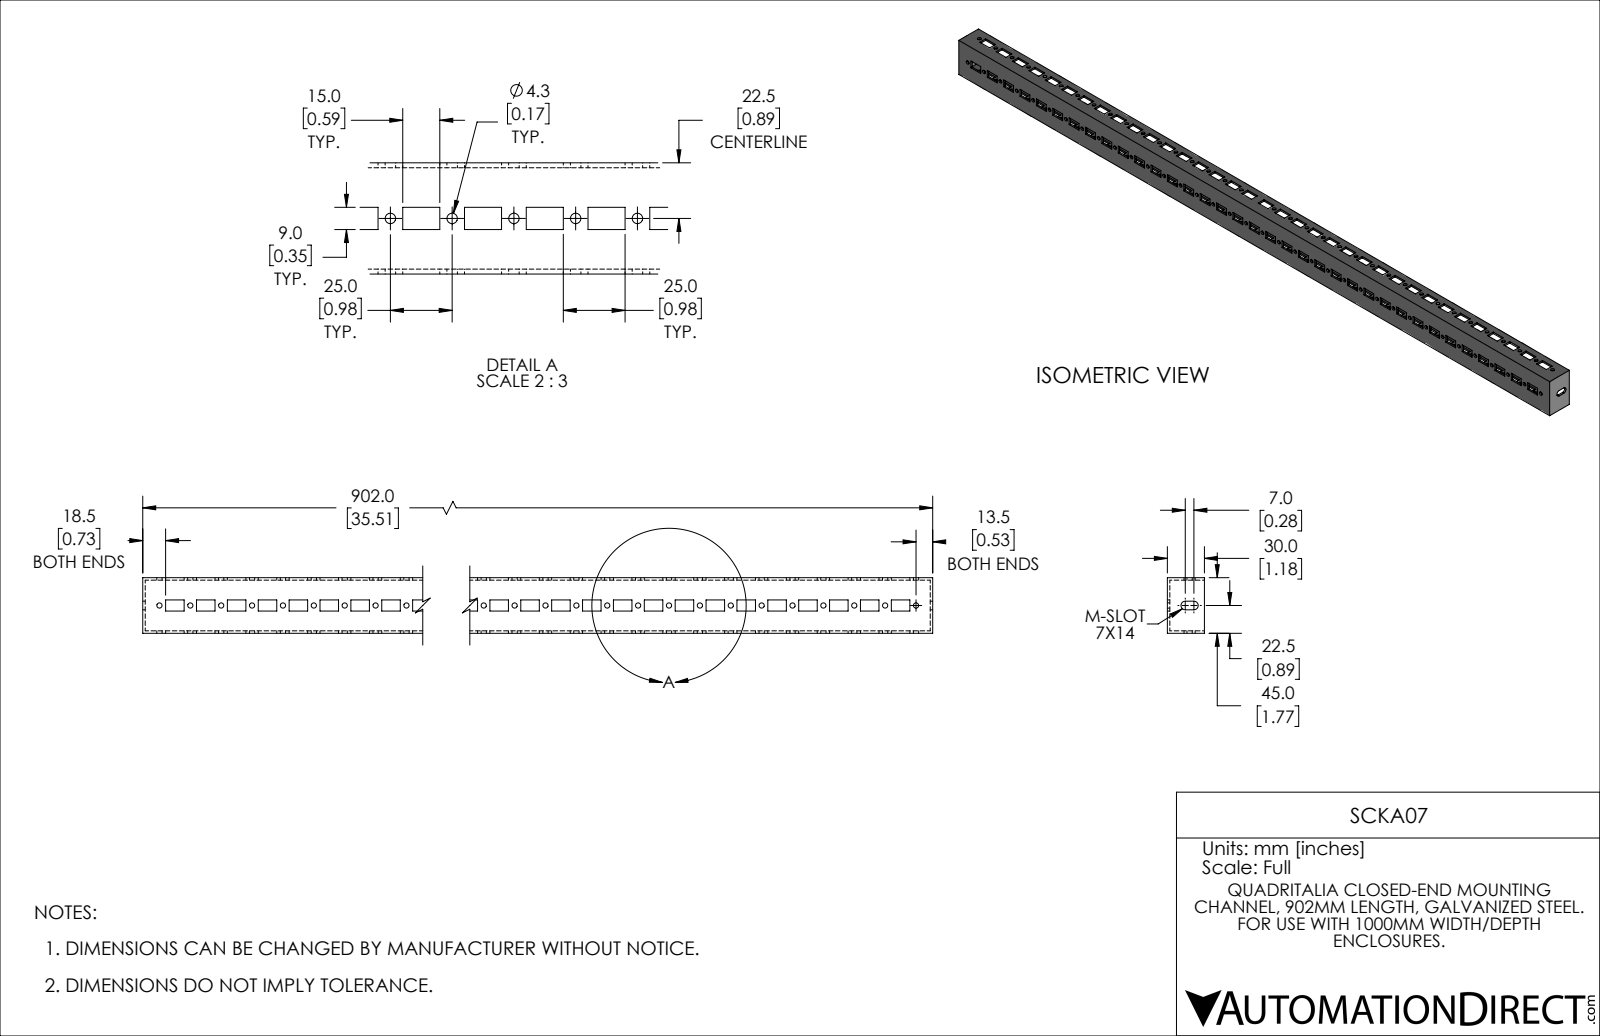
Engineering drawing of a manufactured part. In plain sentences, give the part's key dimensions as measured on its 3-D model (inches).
The part is named "SCKA07". Its 3-D file was written by "SolidWorks 2021 (CONFIG_CONTROL_DESIGN)". It is 1 solid with 545 faces: 435 planar, 110 cylindrical and 0 other. Overall it measures 35.512 by 1.772 by 1.181 inches. Its volume is 9.464 cubic inches and its surface area 266.5 square inches. Round holes: 71 of diameter 0.167. Partial cylindrical surfaces (rounded edges, fillets, slot ends): 2 of radius 0.138. The main face-to-face distances are 0.079, 1.693, 1.772, 1.614, 1.181, 1.102, 0.354, 0.984, 35.433, 0.531. The hole center spacings are 1.969, 0.984, 3.937, 2.953, 4.921, 5.906, 6.89, 7.874.
